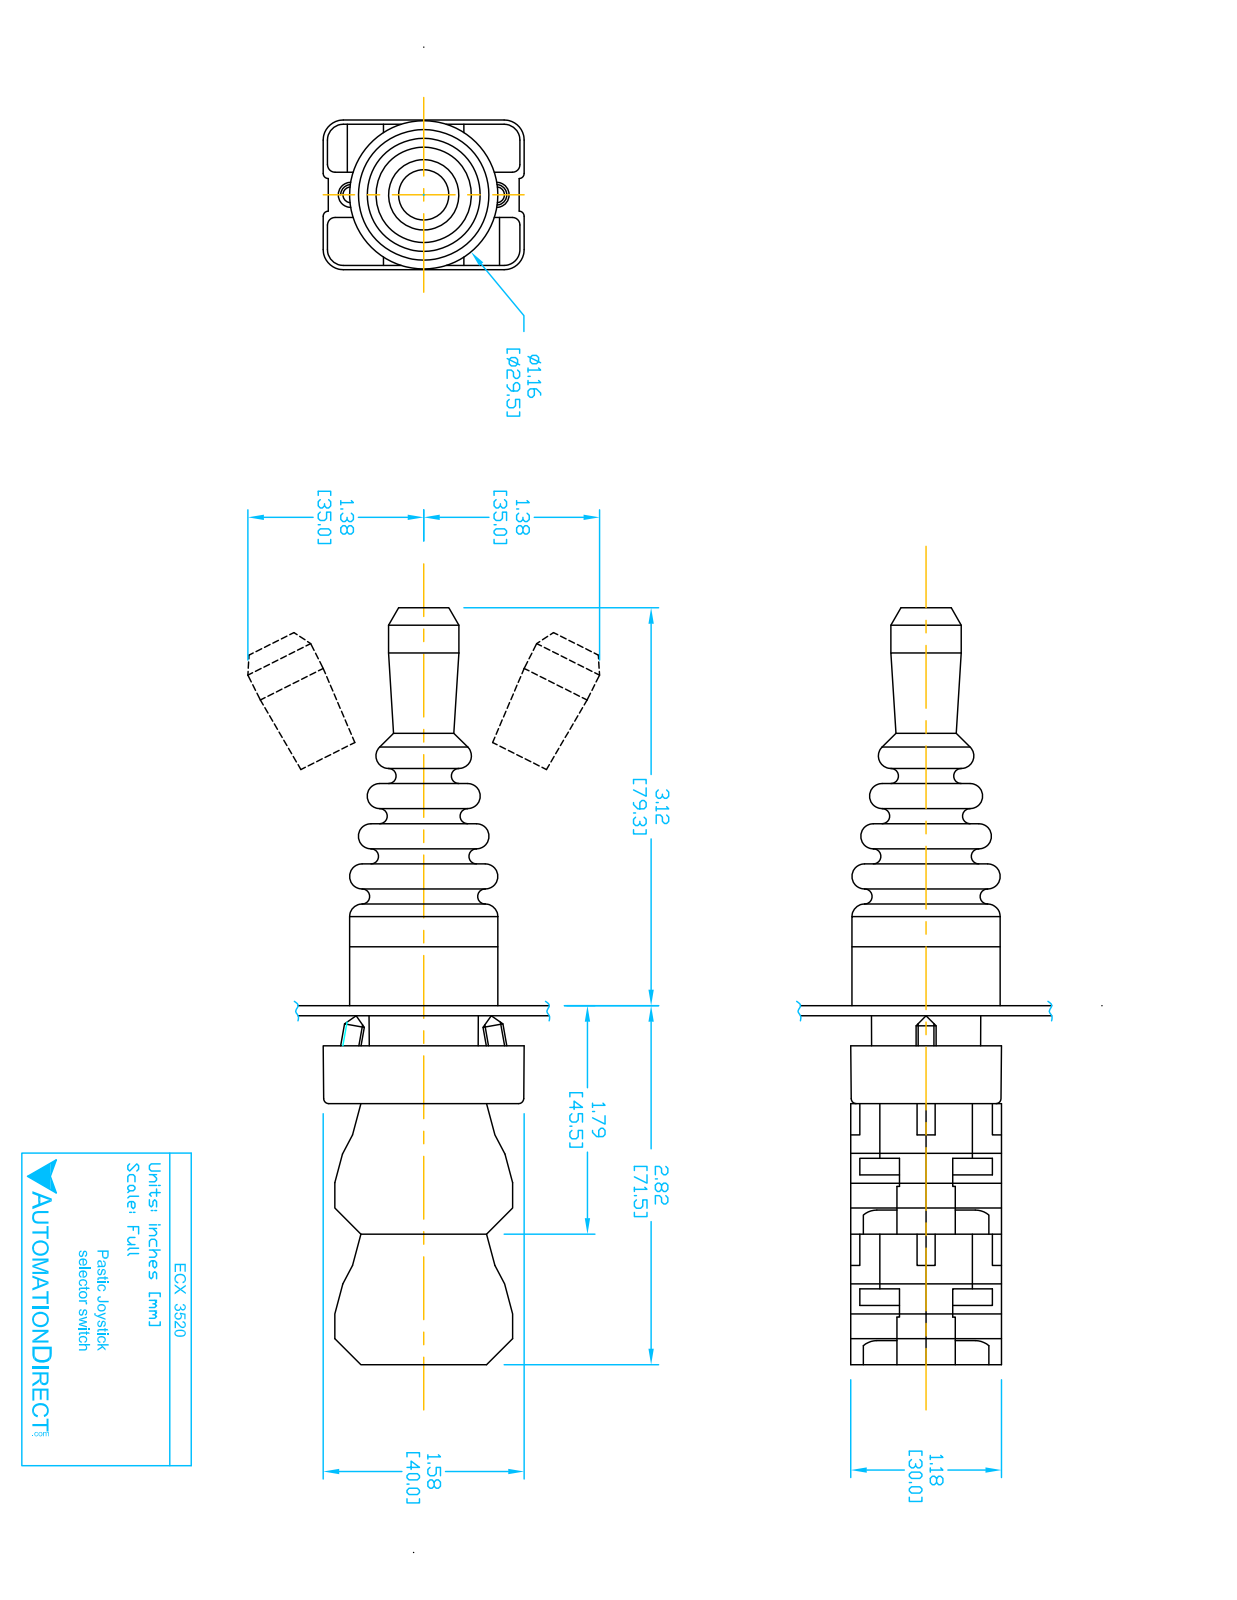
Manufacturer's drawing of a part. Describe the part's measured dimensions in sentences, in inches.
The part is named "ECX3520". Its 3-D file was written by "SolidWorks 2017 (AUTOMOTIVE_DESIGN)". It is 9 solids with 707 faces: 450 planar, 172 cylindrical and 85 other. Overall it measures 5.909 by 1.581 by 1.181 inches. Its volume is 4.87 cubic inches and its surface area 51.32 square inches. Round holes: 4 of diameter 0.079, 2 of diameter 0.087, 2 of diameter 0.124, 2 of diameter 0.13, 1 of diameter 0.197, 1 of diameter 0.878, 1 of diameter 0.888. Round bosses or shafts: 2 of diameter 0.157, 1 of diameter 1.181, 1 of diameter 1.175, 1 of diameter 0.945, 1 of diameter 0.856, 1 of diameter 0.78. Partial cylindrical surfaces (rounded edges, fillets, slot ends): 24 of radius 0.059, 12 of radius 0.041, 12 of radius 0.124, 12 of radius 0.157, 4 of radius 0.02, 4 of radius 0.039, 2 of radius 0.063, 2 of radius 0.079. The main face-to-face distances are 0.579, 0.598, 1.024, 0.02, 1.177, 1.193, 2.217, 0.018, 0.037, 0.031. The hole center spacings are 0.236, 0.98, 0.472, 0.544, 1.004, 1.013, 0.49, 0.491.
